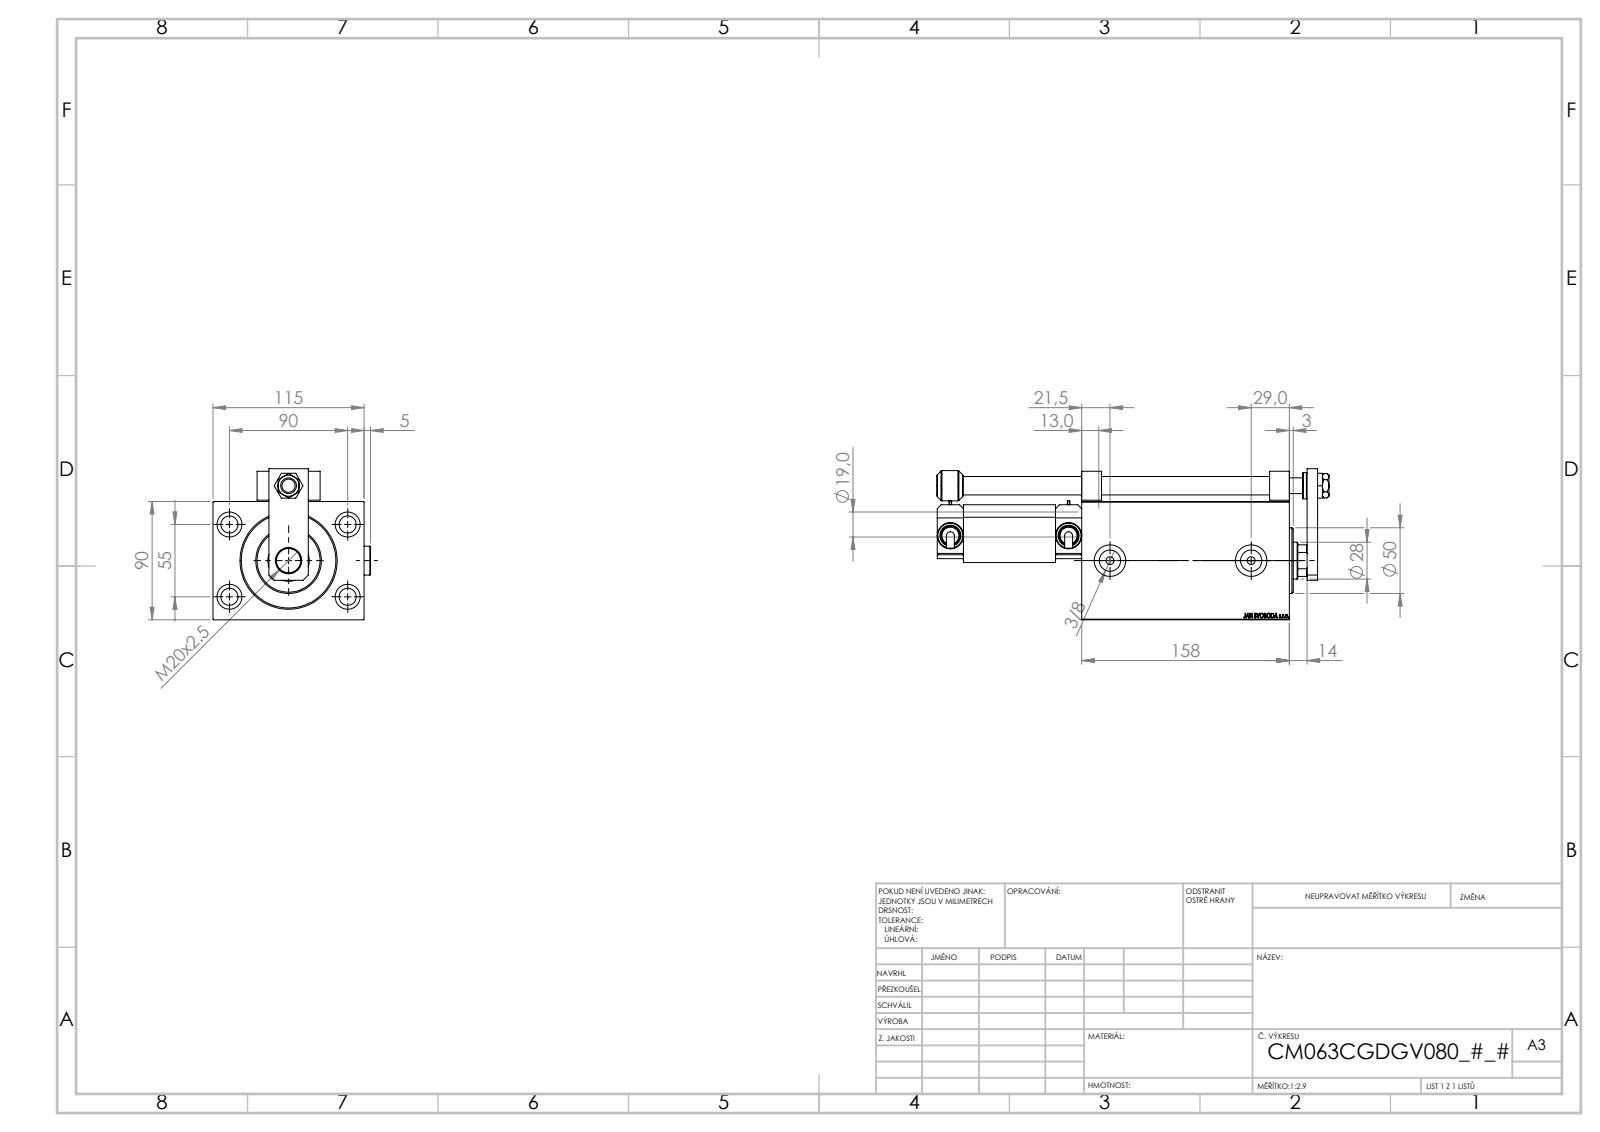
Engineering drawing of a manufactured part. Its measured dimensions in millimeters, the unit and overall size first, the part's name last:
Units: millimetres
Overall size (bounding box): 298.5 × 119.9 × 115
Round holes (diameter × count): ⌀13 ×5, ⌀4 ×4, ⌀8 ×4, ⌀19 ×4, ⌀6 ×2, ⌀16.17 ×2, ⌀24 ×2, ⌀12 ×1, ⌀14 ×1, ⌀18.5 ×1, ⌀20 ×1, ⌀28 ×1
Round bosses / shafts (diameter × count): ⌀20 ×3, ⌀22 ×2, ⌀16 ×2, ⌀14 ×2, ⌀6 ×2, ⌀50 ×1, ⌀23 ×1
Partial cylindrical surfaces — rounded edges, fillets, slot ends (radius × count): R3 ×1, R13.5 ×1
Main face-to-face distances: 90, 115, 37.5, 158, 77.5, 17.5, 140.5, 13.5, 20, 43.5
Hole centre spacings: 52.74, 20, 53.81, 55, 90, 95.74, 105.48, 143
Volume: 1 605 000 mm³ · Surface area: 246 595 mm²
Bodies: 16 solids, 1144 faces (555 planar, 136 cylindrical, 453 other)
Part name (STEP PRODUCT): SWITCH DIM W_B; NUT_D19_P; ZARAZKA_P; TYC_P (+7 more)
STEP written by: SolidWorks 2019 (CONFIG_CONTROL_DESIGN)
